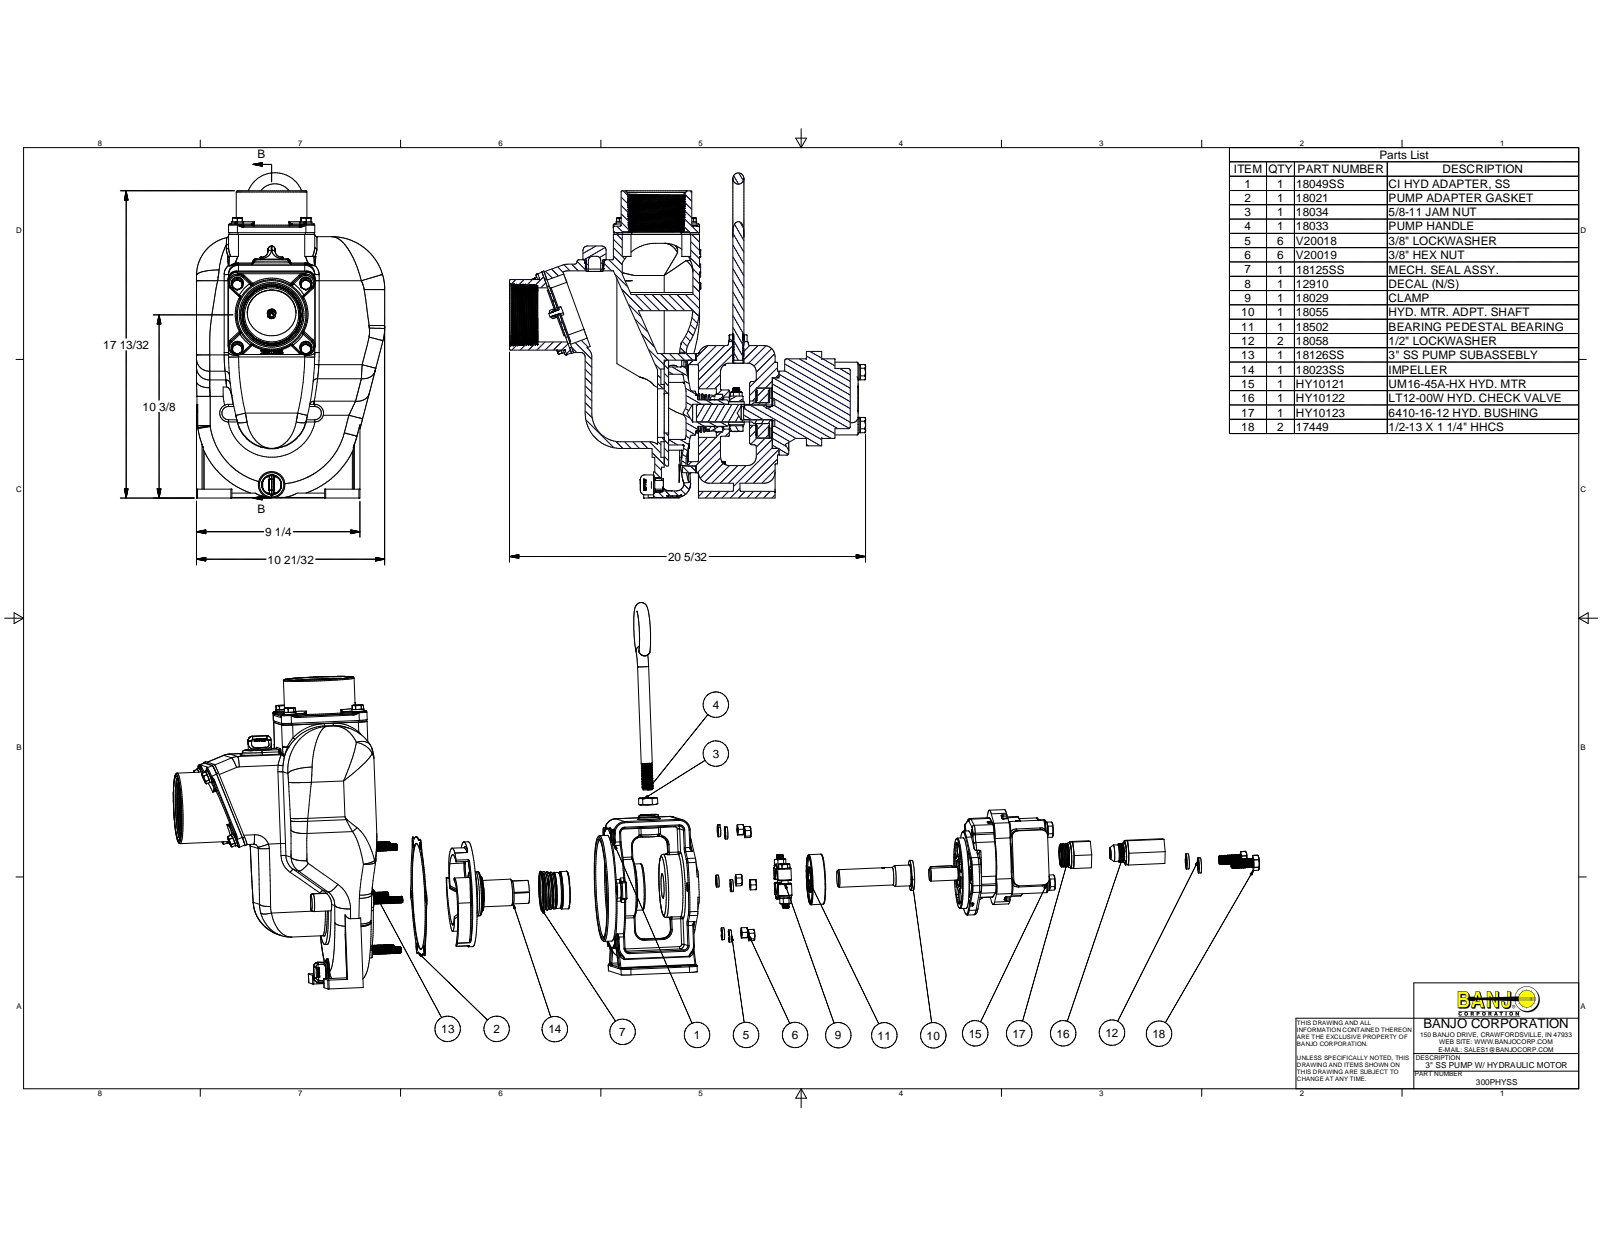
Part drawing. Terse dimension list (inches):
name: 18001SS; 18004SS; 18106SS; V20018 (+8 more)
written by: Autodesk Inventor 2015 (AUTOMOTIVE_DESIGN)
unit: in
bodies: 74 solids, 7392 faces (1572 planar, 2473 cylindrical, 3347 other)
size: 23.024 × 18.433 × 10.65
volume: 424.5 in³; area: 2 534 in²
holes: 22× ⌀0.406, 16× ⌀0.307, 16× ⌀0.385, 14× ⌀0.437, 6× ⌀0.307, 6× ⌀0.375, 4× ⌀0.25, 4× ⌀0.516, 4× ⌀0.56, 4× ⌀0.626, 3× ⌀0.548, 2× ⌀0.281
bosses: 166× ⌀0.324, 46× ⌀0.337, 30× ⌀0.436, 16× ⌀0.687, 12× ⌀0.375, 12× ⌀0.212, 6× ⌀0.5, 6× ⌀0.3
rounds: 162× R0.06, 84× R0.12, 46× R0.25, 41× R0.5, 36× R0.125, 34× R0.03, 30× R0.063, 22× R1
face distances: 0.375, 0.375, 0.125, 0.311, 0.25, 0.5, 2.311, 2, 2.25, 1.75
hole spacings: 3.875, 5.48, 2.74, 3.375, 3.875, 2.74, 1.521, 2.739
